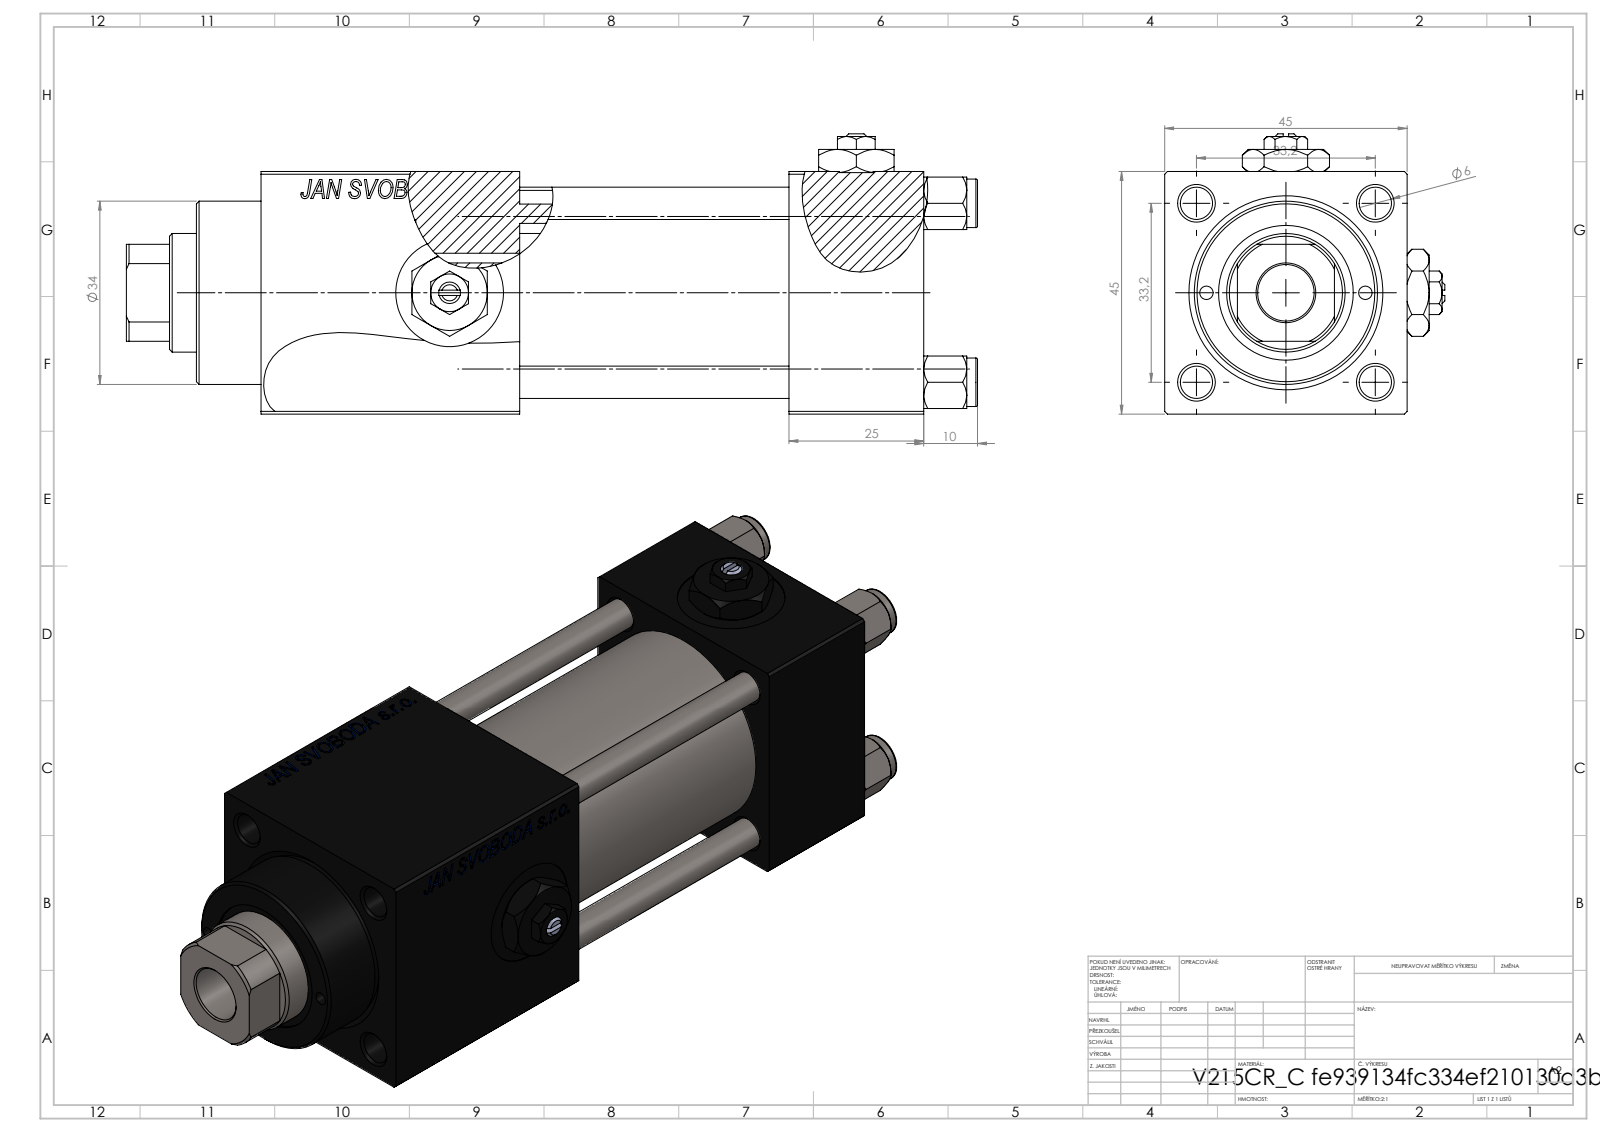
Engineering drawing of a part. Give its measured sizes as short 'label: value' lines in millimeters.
name: V215_VC_A; NUT_M5_C; V215CR_C_TYCINKA; V215CR_C_Body (+2 more)
written by: SolidWorks 2019 (CONFIG_CONTROL_DESIGN)
unit: mm
bodies: 13 solids, 1254 faces (574 planar, 102 cylindrical, 578 other)
size: 158 × 52 × 52
volume: 207 736 mm³; area: 73 475 mm²
holes: 4× ⌀6, 2× ⌀2.5, 2× ⌀7, 2× ⌀13.16, 2× ⌀20, 1× ⌀10.5, 1× ⌀22, 1× ⌀24, 1× ⌀25, 1× ⌀32, 1× ⌀33
bosses: 4× ⌀9, 1× ⌀38, 1× ⌀34
rounds: 1× R10.5
face distances: 45, 25, 50, 123, 75, 98, 44.8, 48, 94.3, 69.3
hole spacings: 16.7, 23.48, 33.2, 35.47, 14.75, 46.95, 29.5
